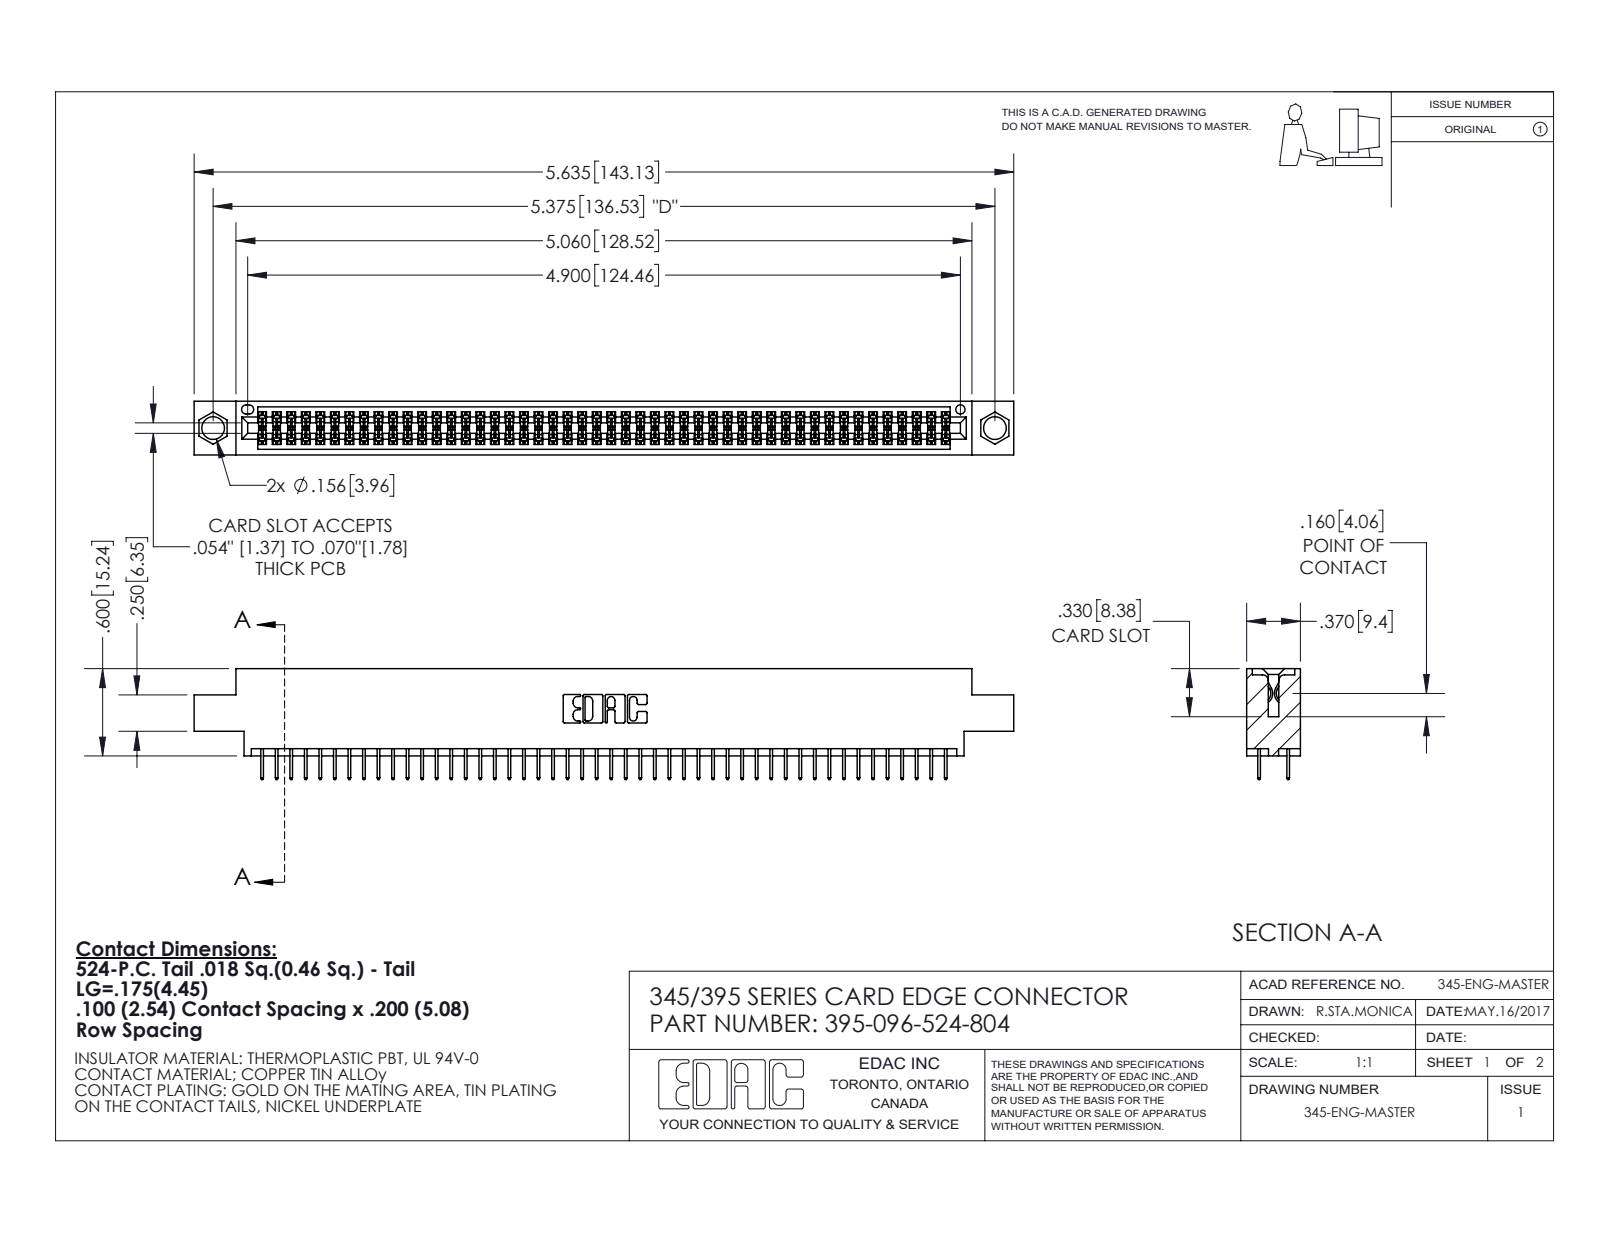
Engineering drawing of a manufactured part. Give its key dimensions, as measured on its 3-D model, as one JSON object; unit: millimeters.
{"part_name": "395-096-524-804; 345-292-001_345-293-124; 345 Part_0.170 Offset - 0.156 Dia-TI", "step_written_by": "SolidWorks 2020 (CONFIG_CONTROL_DESIGN)", "units": "millimeters", "bodies": {"solids": 97, "faces": 5328, "planar": 3842, "cylindrical": 1486, "other": 0}, "overall_size": [143.1, 19.4, 9.4], "volume_mm3": 13600, "surface_area_mm2": 19830, "round_holes": [[4, 2], [1.6, 1]], "partial_cylinders_radius": [[0.2, 144], [0.3, 22], [0.2, 6], [0.8, 6], [0.7, 3], [0.4, 2], [0.5, 2], [0.6, 2]], "face_to_face_distances": [1.8, 7.6, 9.4, 5.1, 2.5, 6.9, 0.6, 5.7, 4.4, 1.8], "hole_center_spacings": [6.9, 130.5, 136.5]}
